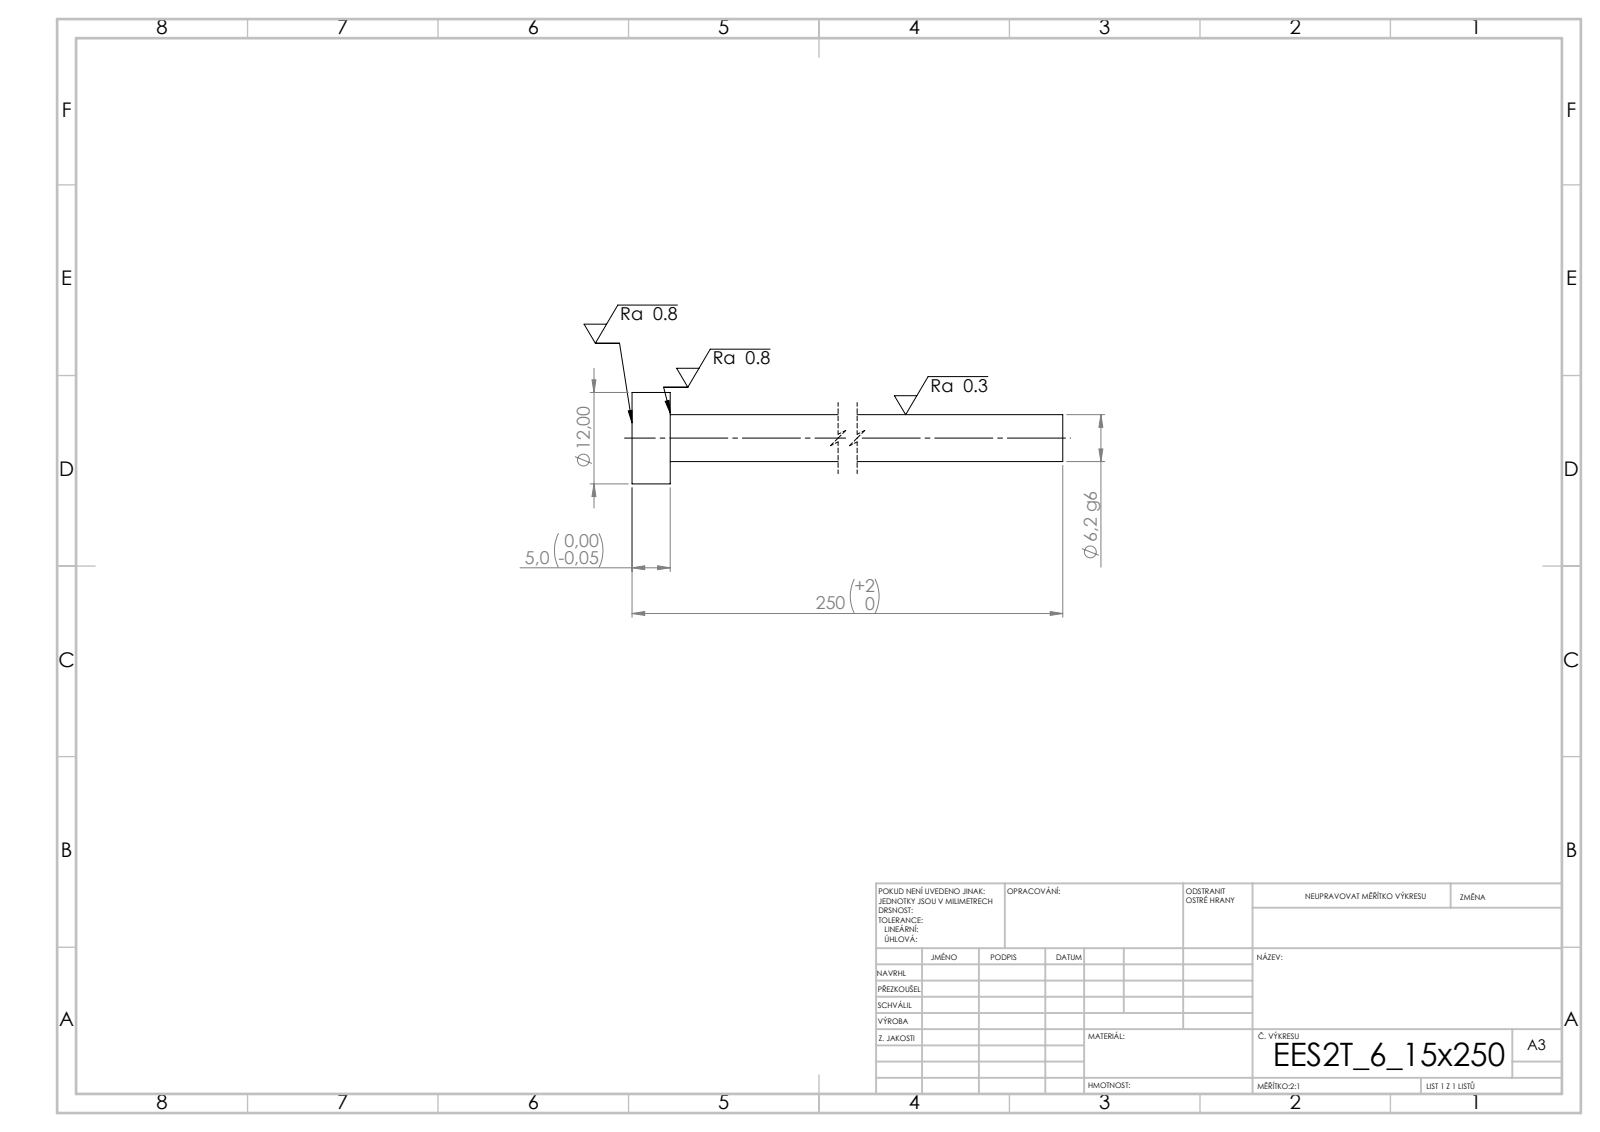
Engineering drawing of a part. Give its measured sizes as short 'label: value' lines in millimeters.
written by: SolidWorks 2019 (CONFIG_CONTROL_DESIGN)
unit: mm
bodies: 1 solid, 7 faces (3 planar, 4 cylindrical, 0 other)
size: 250 × 12 × 12
volume: 7 843 mm³; area: 5 148 mm²
bosses: 1× ⌀12, 1× ⌀6.15
face distances: 5, 250, 245
